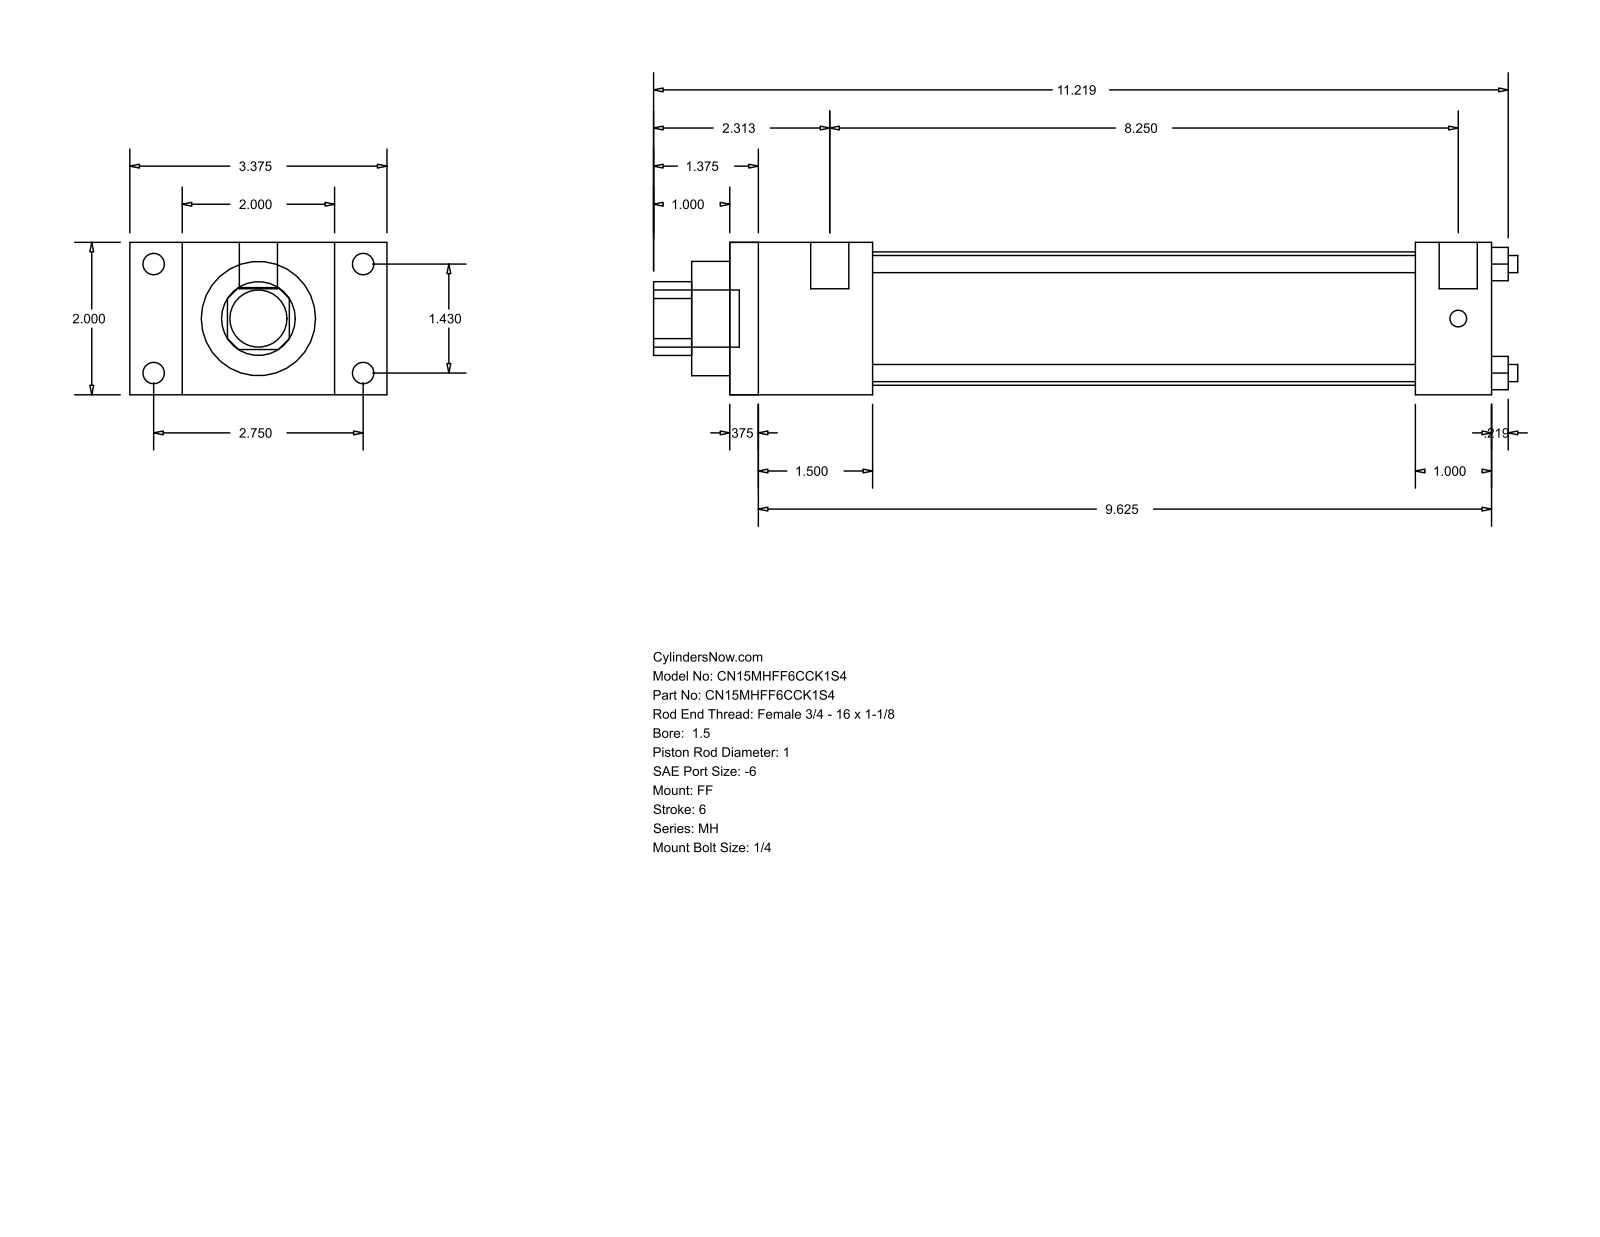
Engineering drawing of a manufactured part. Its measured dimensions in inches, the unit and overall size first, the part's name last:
Units: inches
Overall size (bounding box): 11.344 × 3.375 × 2
Round holes (diameter × count): ⌀0.225 ×4, ⌀1 ×1, ⌀1.5 ×1, ⌀1.75 ×1
Round bosses / shafts (diameter × count): ⌀0.281 ×4, ⌀0.219 ×4, ⌀0.5 ×2, ⌀0.75 ×1
Partial cylindrical surfaces — rounded edges, fillets, slot ends (radius × count): R0.484 ×1
Main face-to-face distances: 2, 10, 0.375, 9.625, 1, 0.687, 2.687, 1.875, 1.5, 8.125
Hole centre spacings: 1.011, 1.43, 2.022
Bodies: 0 solids, 92 faces (64 planar, 28 cylindrical, 0 other)
Part name (STEP PRODUCT): MH_FF__0150_1
STEP written by: GSSL Pune (CONFIG_CONTROL_DESIGN)
